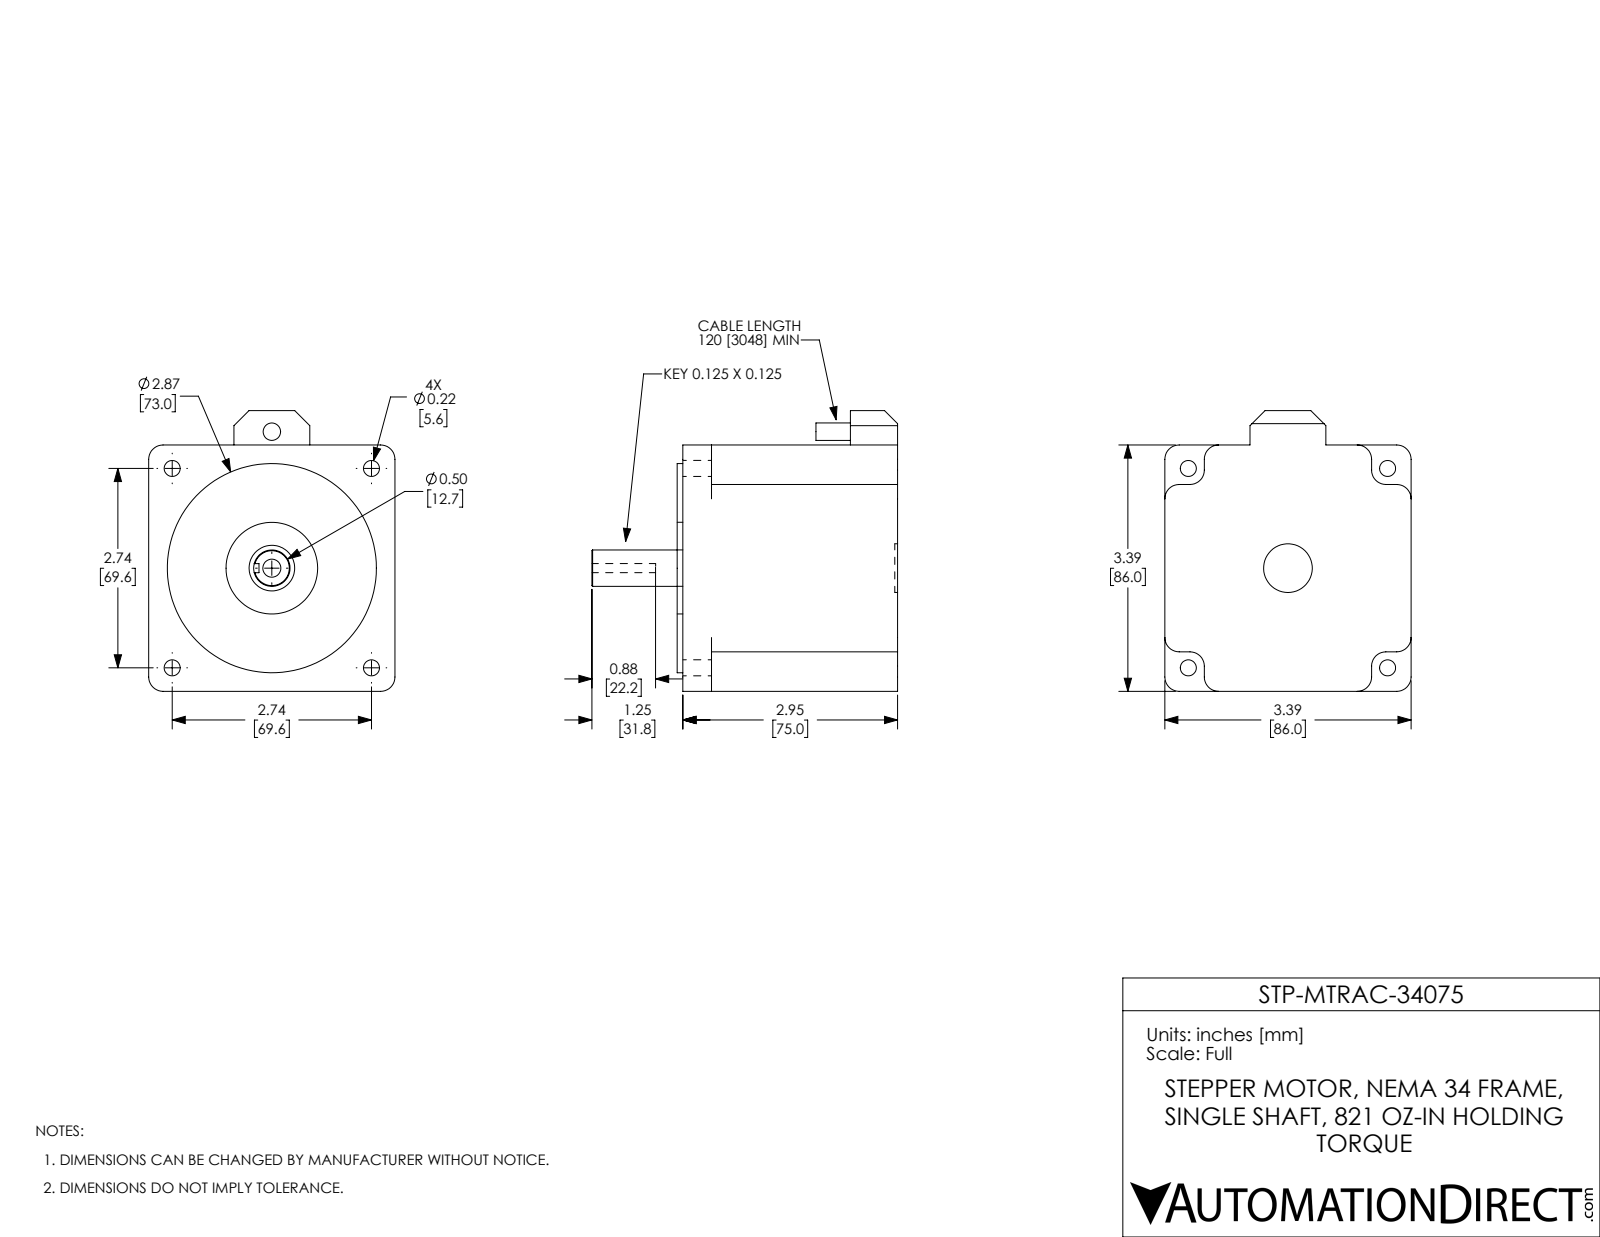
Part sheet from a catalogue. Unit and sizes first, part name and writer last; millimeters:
Units: millimetres
Overall size (bounding box): 106.8 × 98 × 86
Round holes (diameter × count): ⌀5.6 ×4, ⌀17 ×1, ⌀32 ×1
Round bosses / shafts (diameter × count): ⌀73 ×1, ⌀12.7 ×1, ⌀6.1 ×1
Partial cylindrical surfaces — rounded edges, fillets, slot ends (radius × count): R5 ×16
Main face-to-face distances: 86, 75, 77, 2, 13.8, 72.2, 58.4, 12, 65, 10
Hole centre spacings: 49.2, 69.6, 98.4
Volume: 518 000 mm³ · Surface area: 42 390 mm²
Bodies: 1 solid, 71 faces (34 planar, 34 cylindrical, 3 other)
Part name (STEP PRODUCT): STP-MTRAC-34075 from HT34-695 75mm from 696_117mm r1
STEP written by: SolidWorks 2017 (AUTOMOTIVE_DESIGN)
